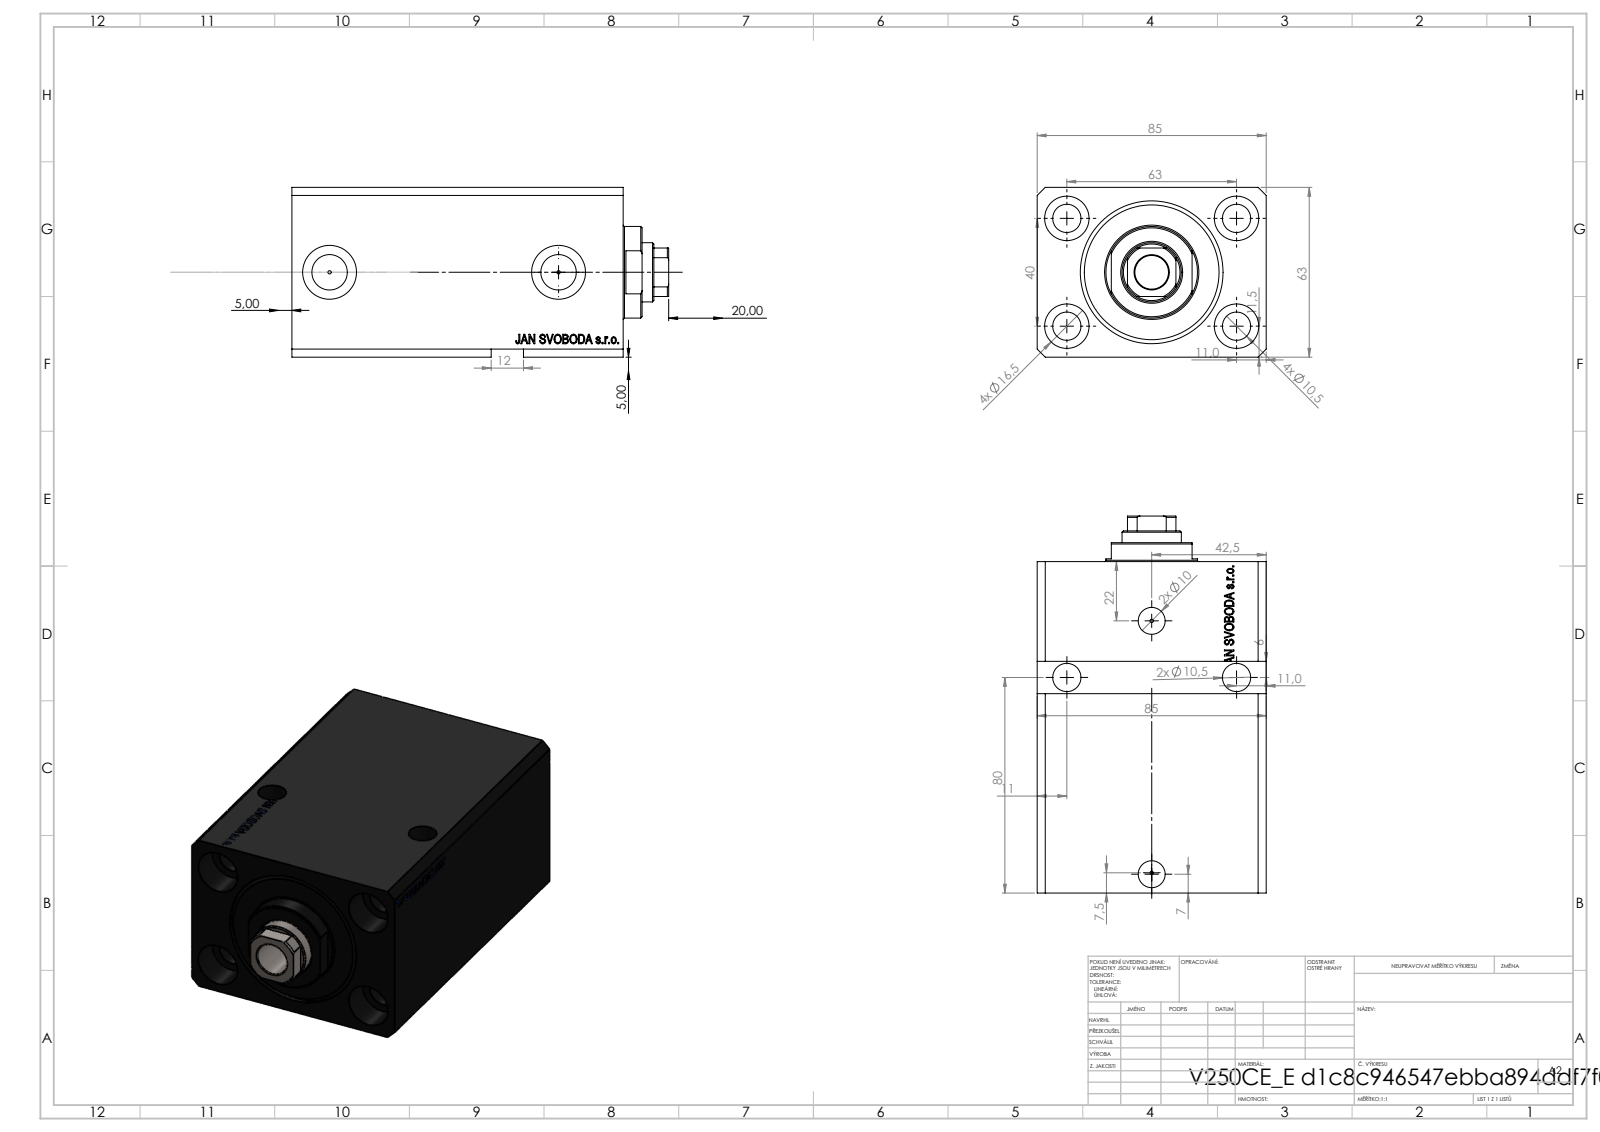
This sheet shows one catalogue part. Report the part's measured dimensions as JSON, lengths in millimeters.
{"part_name": "V250CE_VC_E; V250CE_C_VCP; V250CE_E_Body", "step_written_by": "SolidWorks 2019 (CONFIG_CONTROL_DESIGN)", "units": "millimeters", "bodies": {"solids": 3, "faces": 937, "planar": 459, "cylindrical": 104, "other": 374}, "overall_size": [140, 85, 63], "volume_mm3": 542774, "surface_area_mm2": 107764, "round_holes": [[10.5, 8], [1.25, 4], [16.5, 4], [10, 2], [13.16, 2], [20, 2], [12.5, 1], [22, 1], [40, 1], [53, 1]], "round_bosses_or_shafts": [[34, 1]], "partial_cylinders_radius": [[10.5, 1]], "face_to_face_distances": [63, 85, 123, 17, 106, 11.4, 94.6, 111.6, 56, 11], "hole_center_spacings": [37.31, 63, 37.86, 40, 41.8, 42.15, 45, 73.13]}
